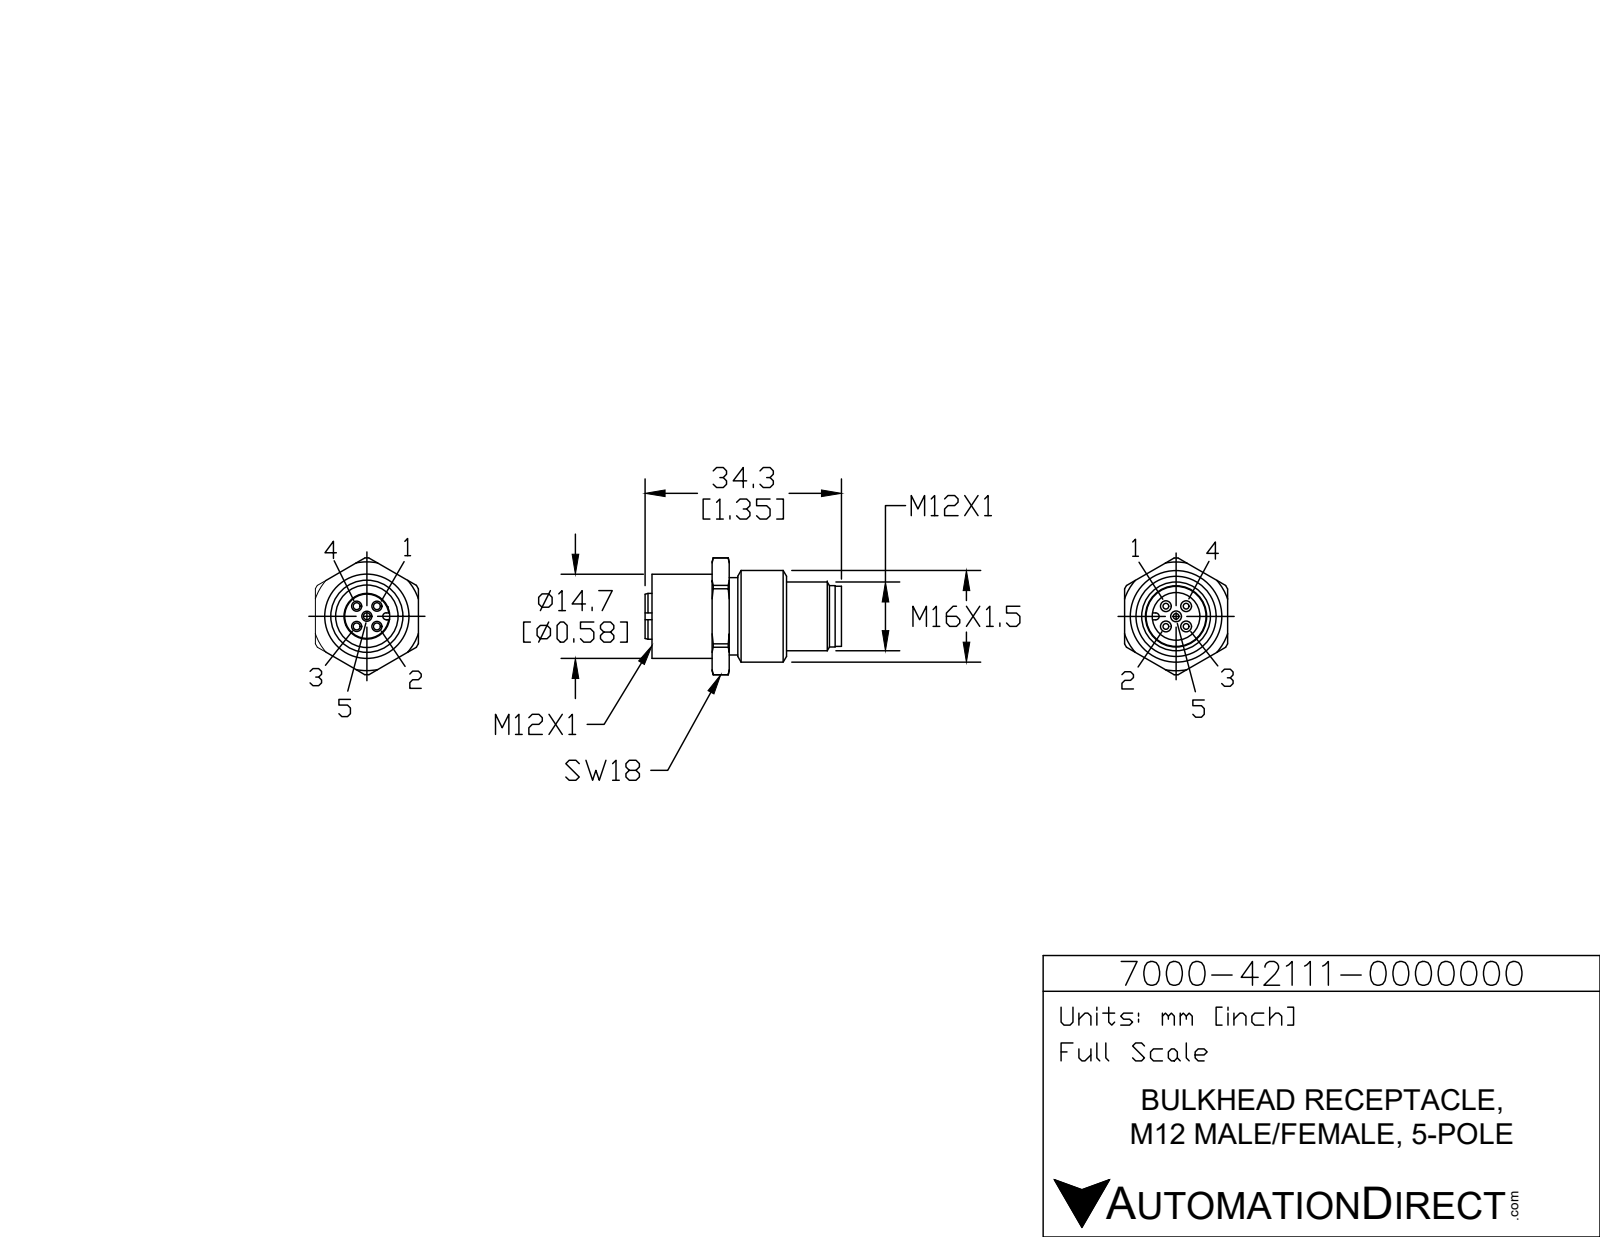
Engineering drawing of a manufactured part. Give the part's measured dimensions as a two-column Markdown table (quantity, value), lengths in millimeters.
| quantity | value |
| --- | --- |
| part name | 7000-42111--0000000 |
| STEP written by | SolidWorks 2015 (AUTOMOTIVE_DESIGN) |
| units | millimeters |
| bodies | 1 solid, 146 faces (37 planar, 62 cylindrical, 47 other) |
| overall size | 34.3 × 20.4 × 18 |
| volume | 4 739 mm³ |
| surface area | 3 178 mm² |
| round holes (diameter × count) | 1.2 × 5, 1.9 × 5, 8.3 × 1, 10.9 × 1 |
| round bosses / shafts (diameter × count) | 1 × 5, 16 × 1, 14.7 × 1, 13.5 × 1, 12 × 1, 10.7 × 1, 10.5 × 1, 8 × 1 |
| partial cylindrical surfaces (radius × count) | 0.2 × 2, 0.6 × 2, 10.2 × 1 |
| main face-to-face distances | 3, 18, 10, 7.8, 10.5, 13.5, 2.7, 5.7, 1.2, 23.5 |
| hole center spacings | 2.5, 3.54, 5.01 |
